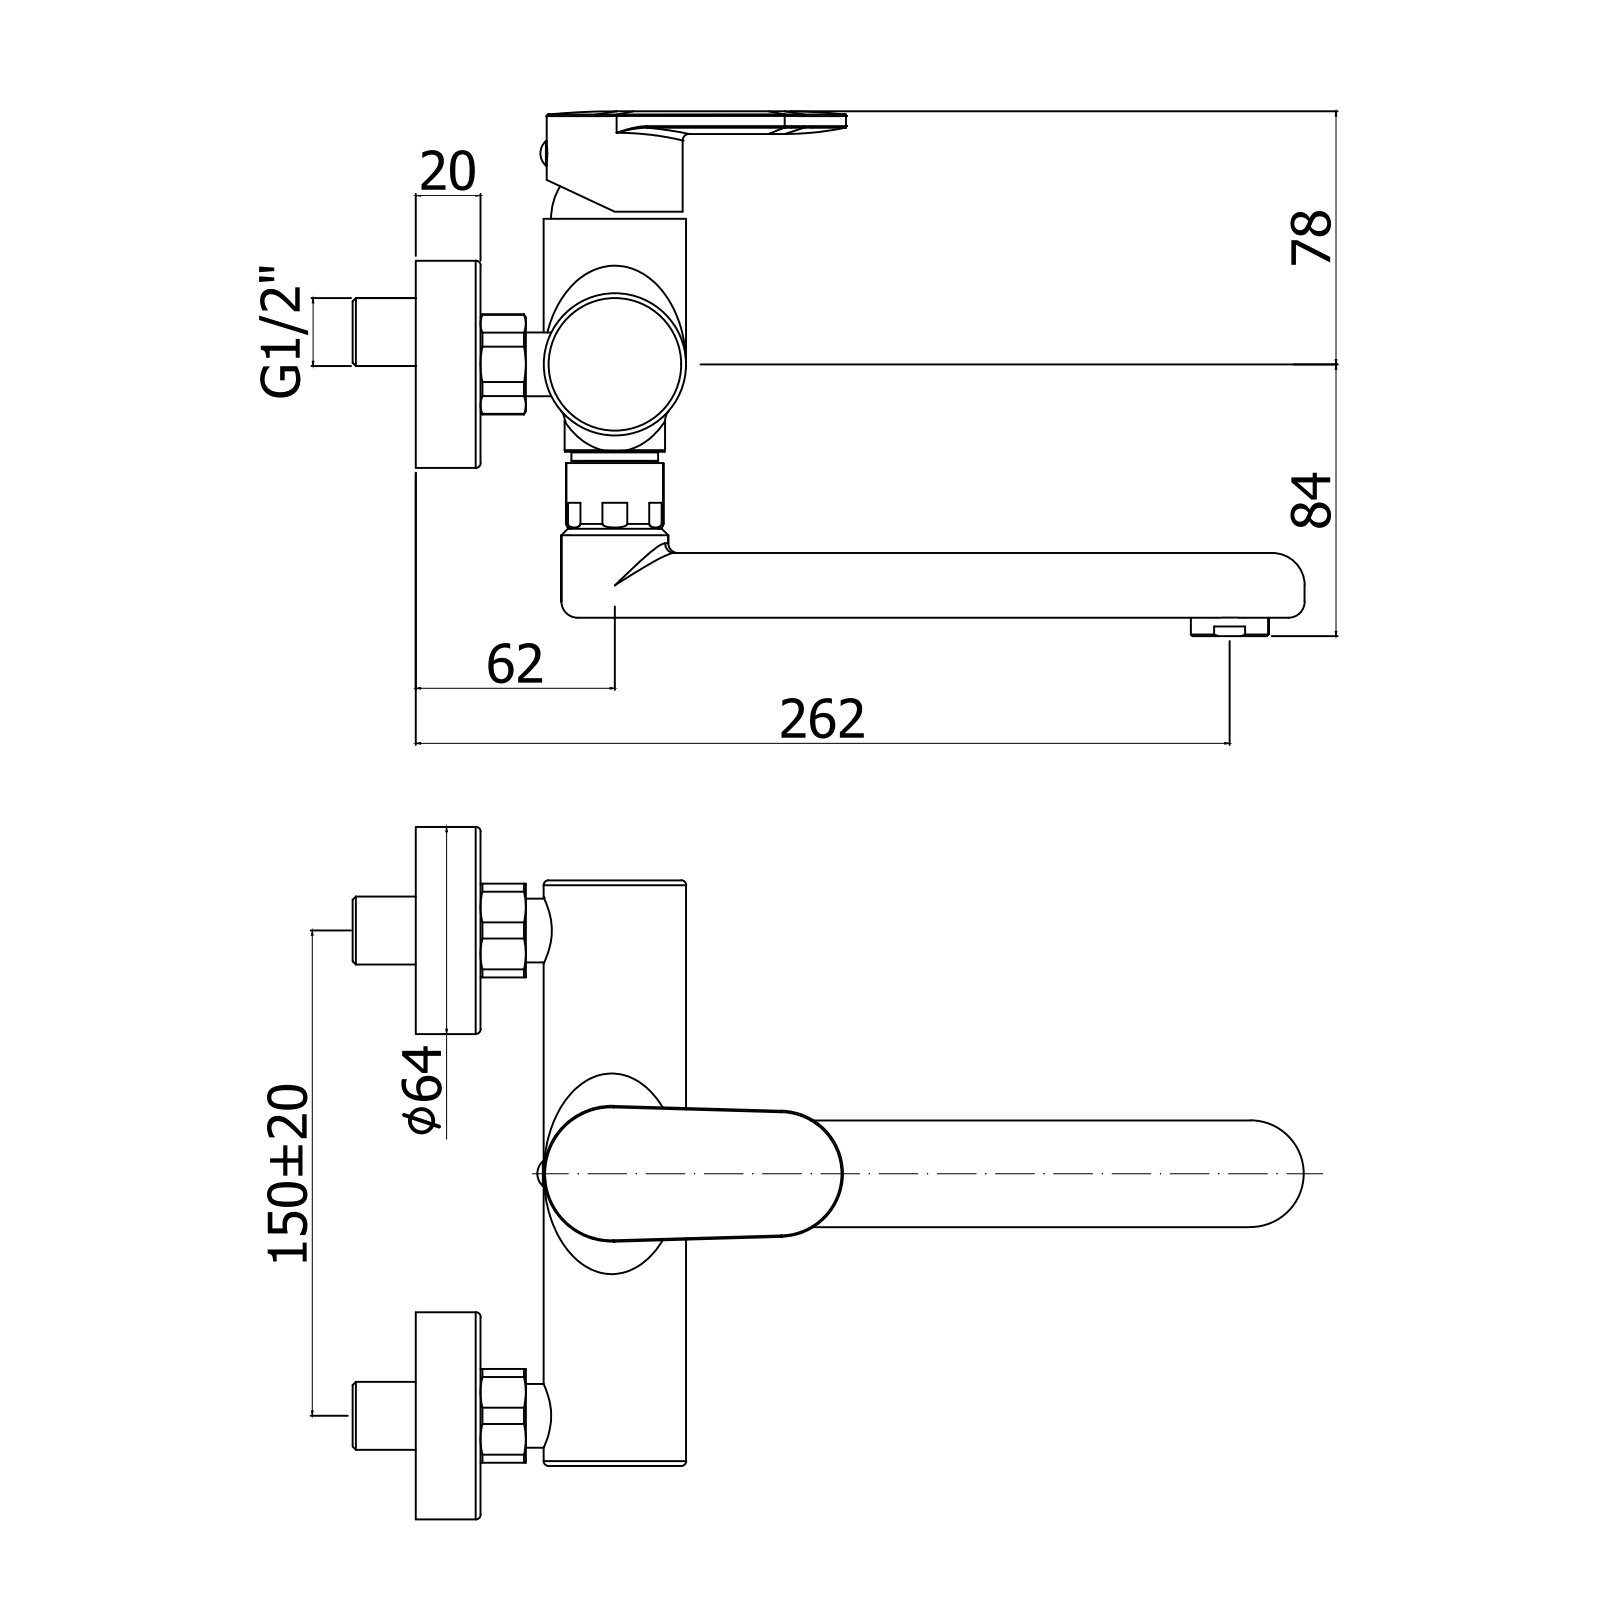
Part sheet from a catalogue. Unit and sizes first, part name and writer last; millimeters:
Units: millimetres
Overall size (bounding box): 271.5 × 213.5 × 152.5
Round holes (diameter × count): ⌀5 ×2, ⌀7 ×2, ⌀10.5 ×2, ⌀20.5 ×2, ⌀23 ×2, ⌀26 ×2, ⌀36.5 ×2, ⌀3 ×1, ⌀4.5 ×1, ⌀14.9 ×1, ⌀16.5 ×1, ⌀17 ×1
Round bosses / shafts (diameter × count): ⌀63.5 ×2, ⌀44 ×2, ⌀28 ×2, ⌀19.7 ×2, ⌀9 ×2, ⌀43 ×1, ⌀31 ×1, ⌀30 ×1
Partial cylindrical surfaces — rounded edges, fillets, slot ends (radius × count): R3 ×4, R7 ×2, R8 ×2, R15.5 ×2, R3.5 ×1, R4.5 ×1, R10 ×1, R20 ×1
Main face-to-face distances: 15, 1, 20, 14, 16, 68.5, 47.5, 112.5, 3.25, 177.75
Hole centre spacings: 8.6, 13.45, 15.13, 21.93, 97.31, 195.13, 210.19, 14
Volume: 328 968 mm³ · Surface area: 145 153 mm²
Bodies: 4 solids, 1339 faces (1047 planar, 144 cylindrical, 148 other)
Part name (STEP PRODUCT): CA161CR
STEP written by: CREO PARAMETRIC BY PTC INC, 2020044 (CONFIG_CONTROL_DESIGN)
